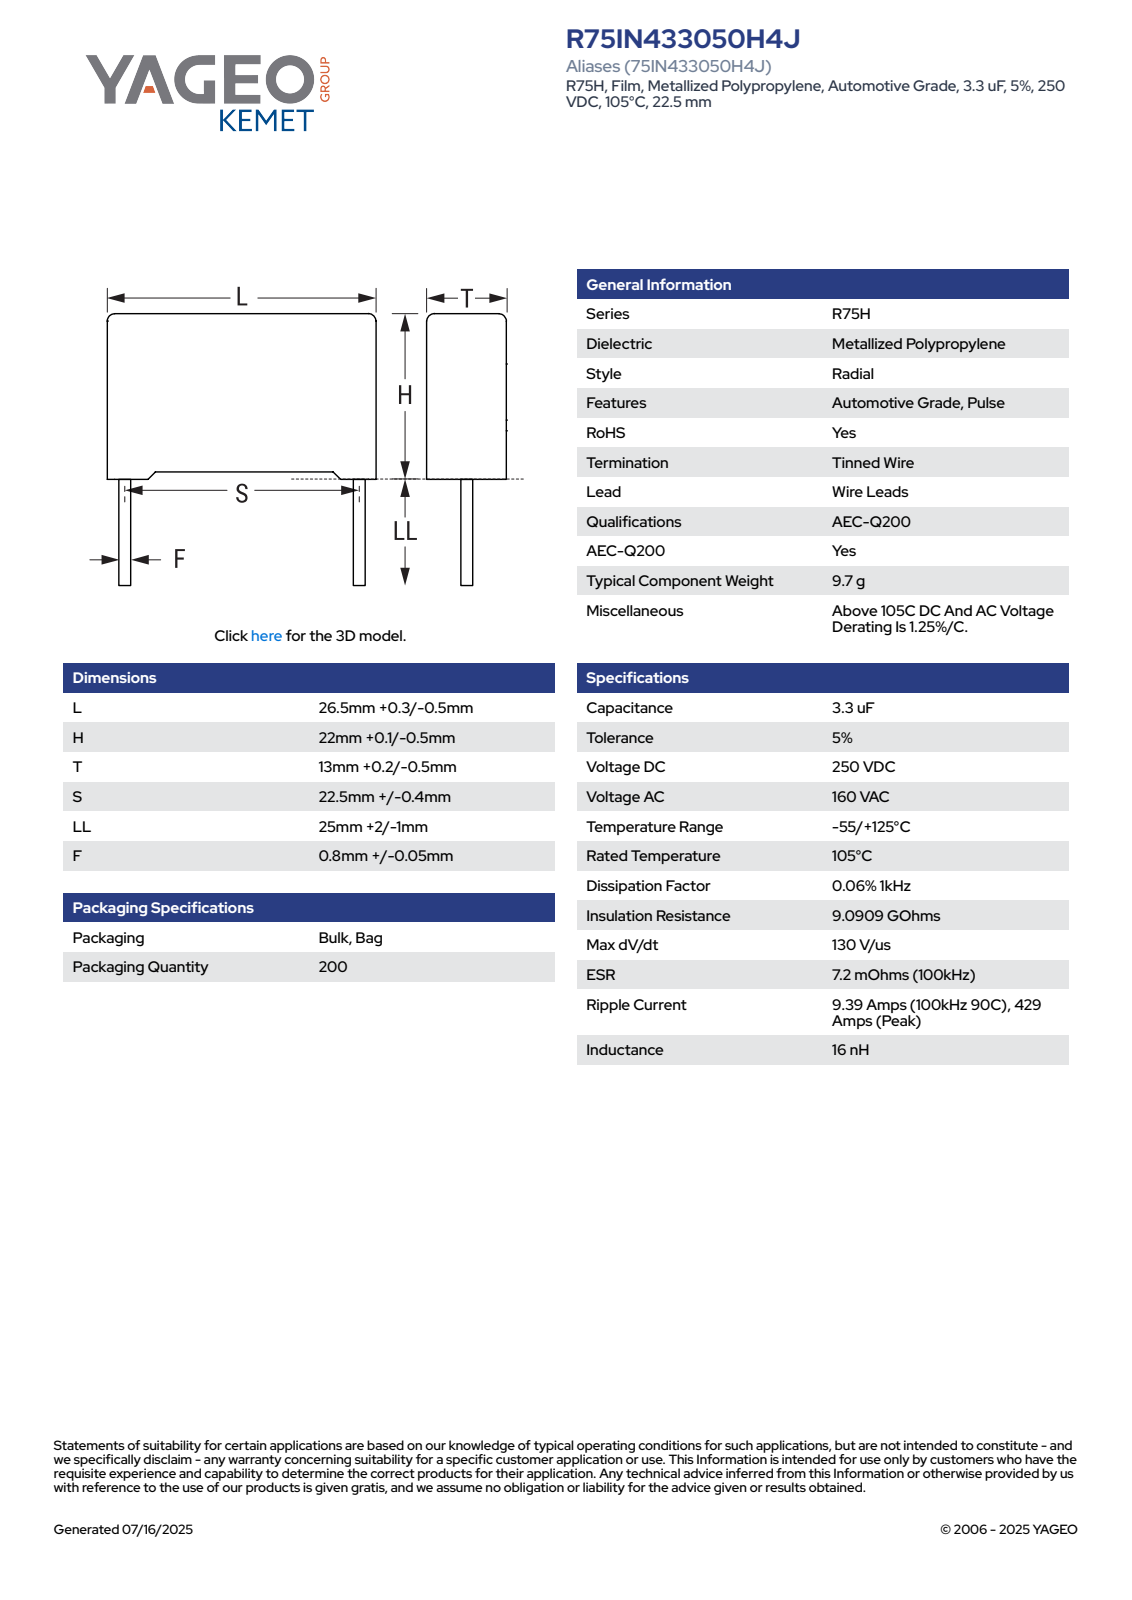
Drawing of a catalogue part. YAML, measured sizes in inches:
part_name: "CFR_RB2_26.5X22X13_L26.8H22.1T13.2S22.5LL27F0.85"
step_written_by: "SolidWorks 2021 (AUTOMOTIVE_DESIGN)"
units: inches
bodies: {solids: 4, faces: 85, planar: 77, cylindrical: 8, other: 0}
overall_size: [1.933, 1.055, 0.52]
volume: 0.464
surface_area: 4.121
round_bosses_or_shafts:
  - {diameter: 0.033, count: 2}
partial_cylinders:
  - {radius: 0.02, count: 4}
face_to_face_distances: [0.52, 1.055, 0.84, 0.841, 0.03, 0.03, 0.87, 0.035, 1.02, 0.52]
